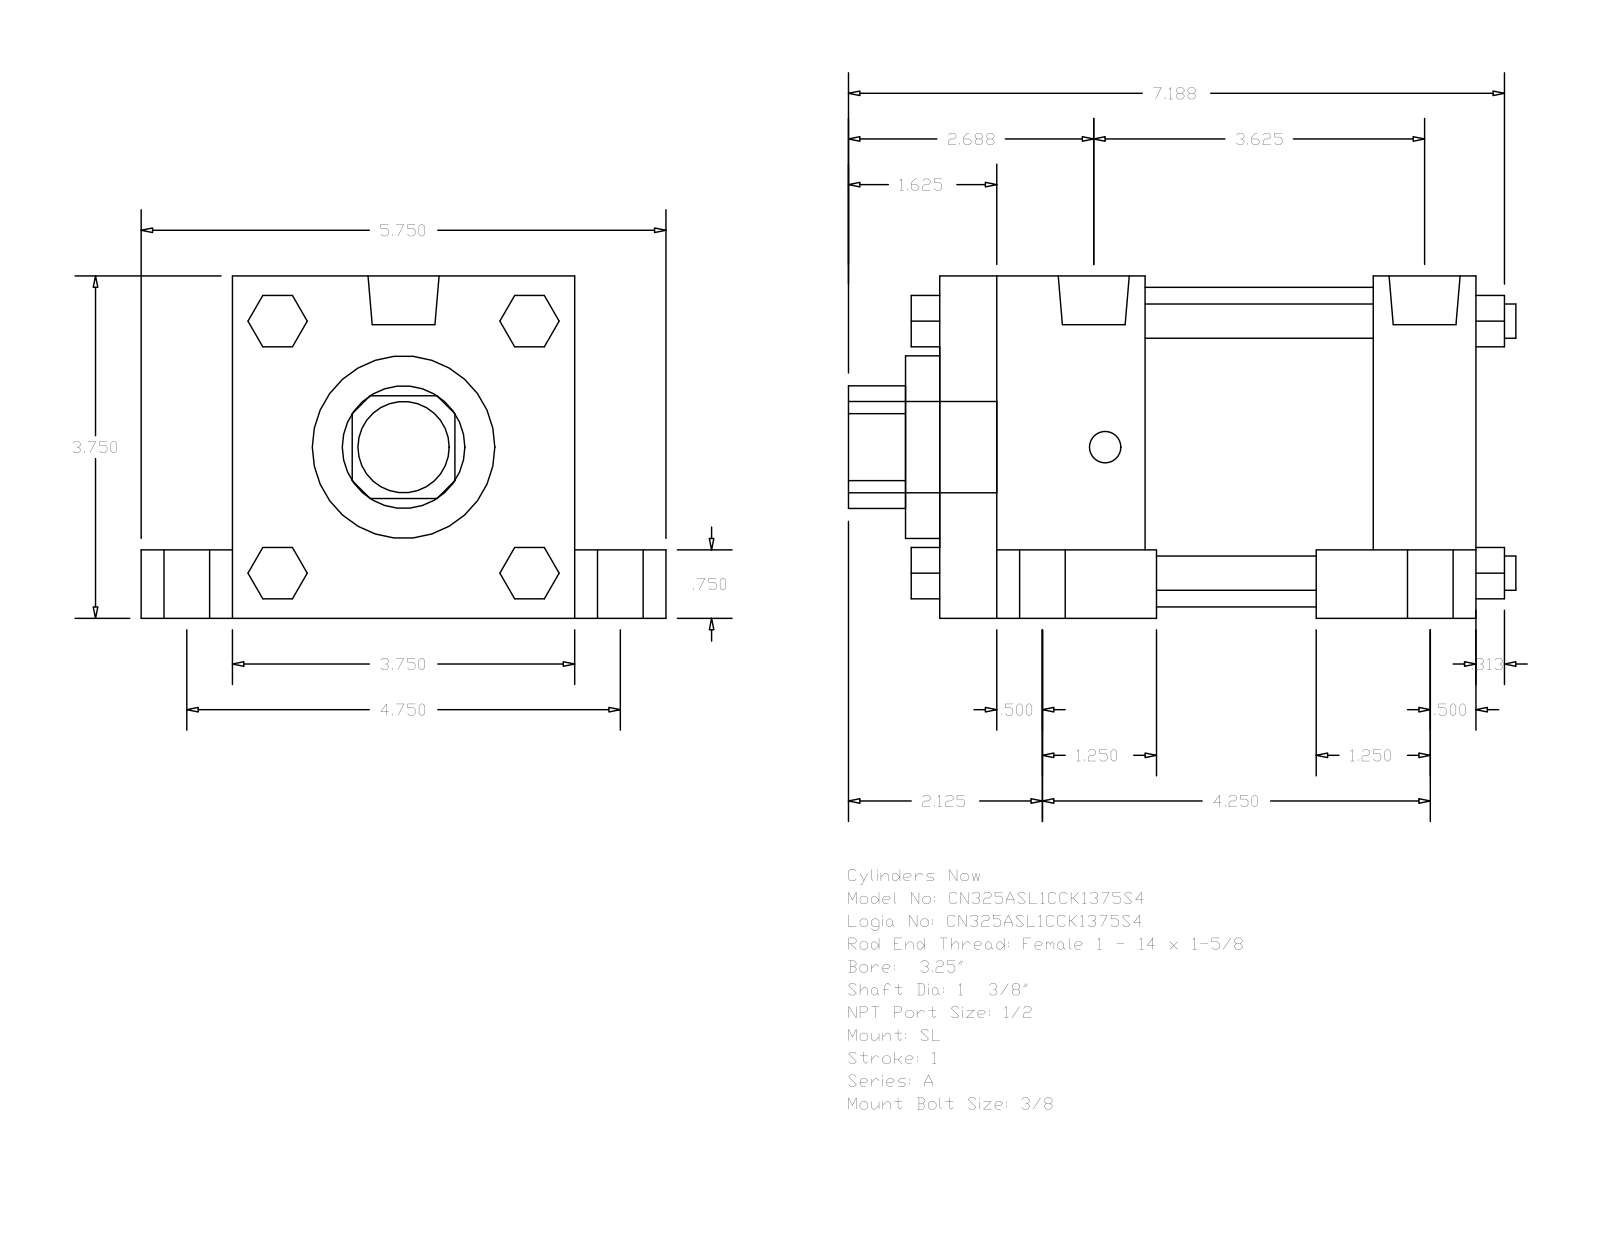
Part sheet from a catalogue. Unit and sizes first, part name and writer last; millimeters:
Units: millimetres
Overall size (bounding box): 185.74 × 146.05 × 95.25
Round holes (diameter × count): ⌀34.92 ×1, ⌀50.8 ×1, ⌀88.9 ×1
Round bosses / shafts (diameter × count): ⌀19.05 ×4, ⌀12.7 ×4, ⌀9.53 ×4, ⌀8.73 ×4, ⌀19.77 ×2, ⌀25.4 ×1
Partial cylindrical surfaces — rounded edges, fillets, slot ends (radius × count): R17.06 ×1
Main face-to-face distances: 95.24, 149.22, 120.65, 25.41, 19.05, 76.19, 15.87, 28.57, 57.15, 63.5
Bodies: 0 solids, 150 faces (114 planar, 36 cylindrical, 0 other)
Part name (STEP PRODUCT): A_SL__0325_1.375
STEP written by: GSSL Pune (CONFIG_CONTROL_DESIGN)
